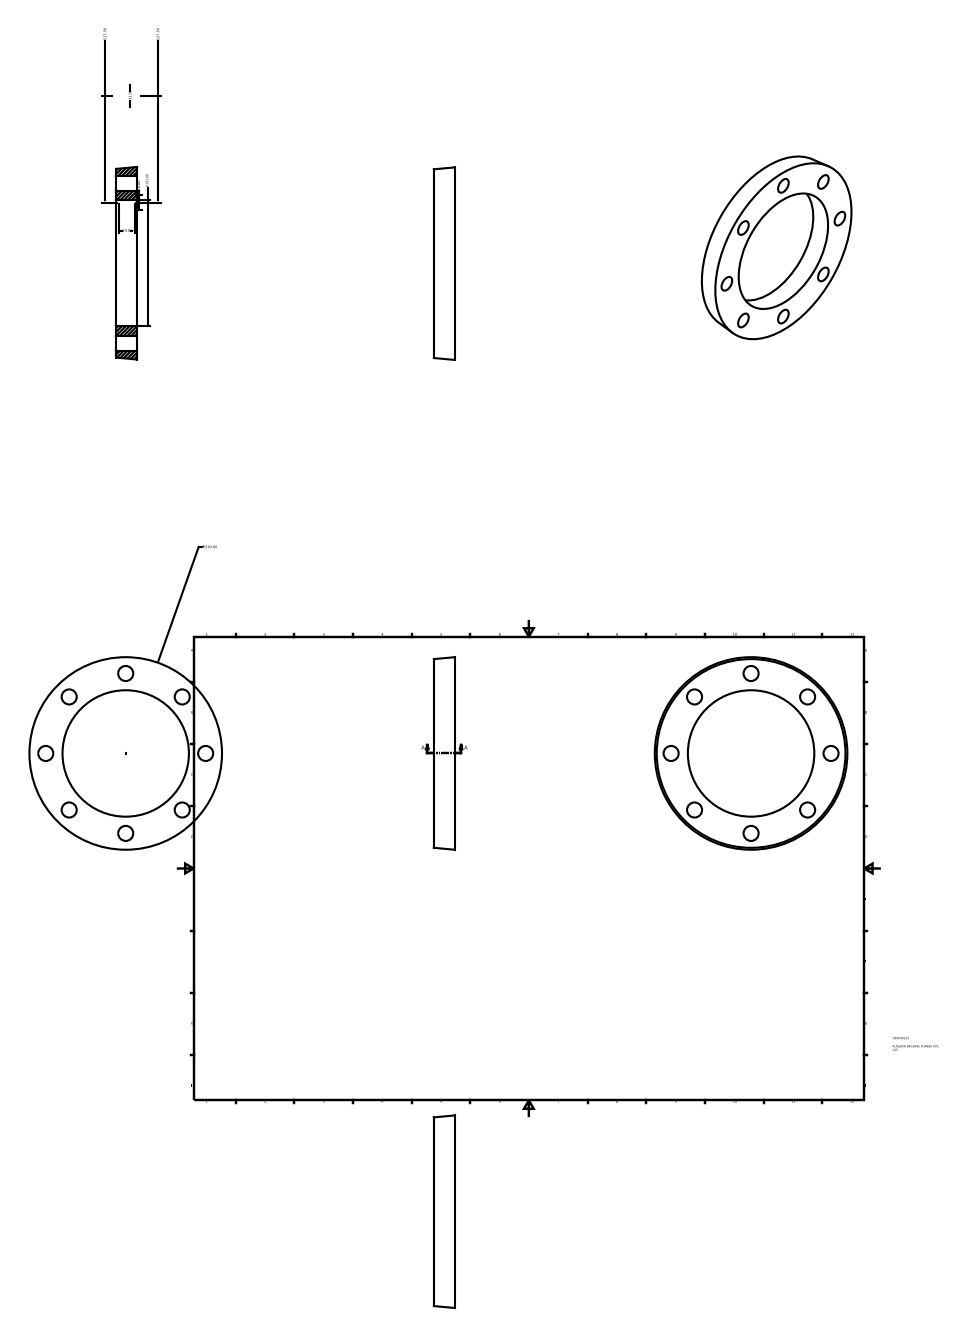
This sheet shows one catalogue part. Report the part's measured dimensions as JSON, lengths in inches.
{"part_name": "059000125", "step_written_by": "Autodesk Inventor 2015 (AUTOMOTIVE_DESIGN)", "units": "inches", "bodies": {"solids": 1, "faces": 12, "planar": 2, "cylindrical": 9, "other": 1}, "overall_size": [9.055, 9.055, 0.984], "volume_in3": 31.7, "surface_area_in2": 128.2, "round_holes": [[0.709, 8], [5.945, 1]], "face_to_face_distances": [0.984], "hole_center_spacings": [2.878, 3.76, 5.317, 6.947, 7.52]}
